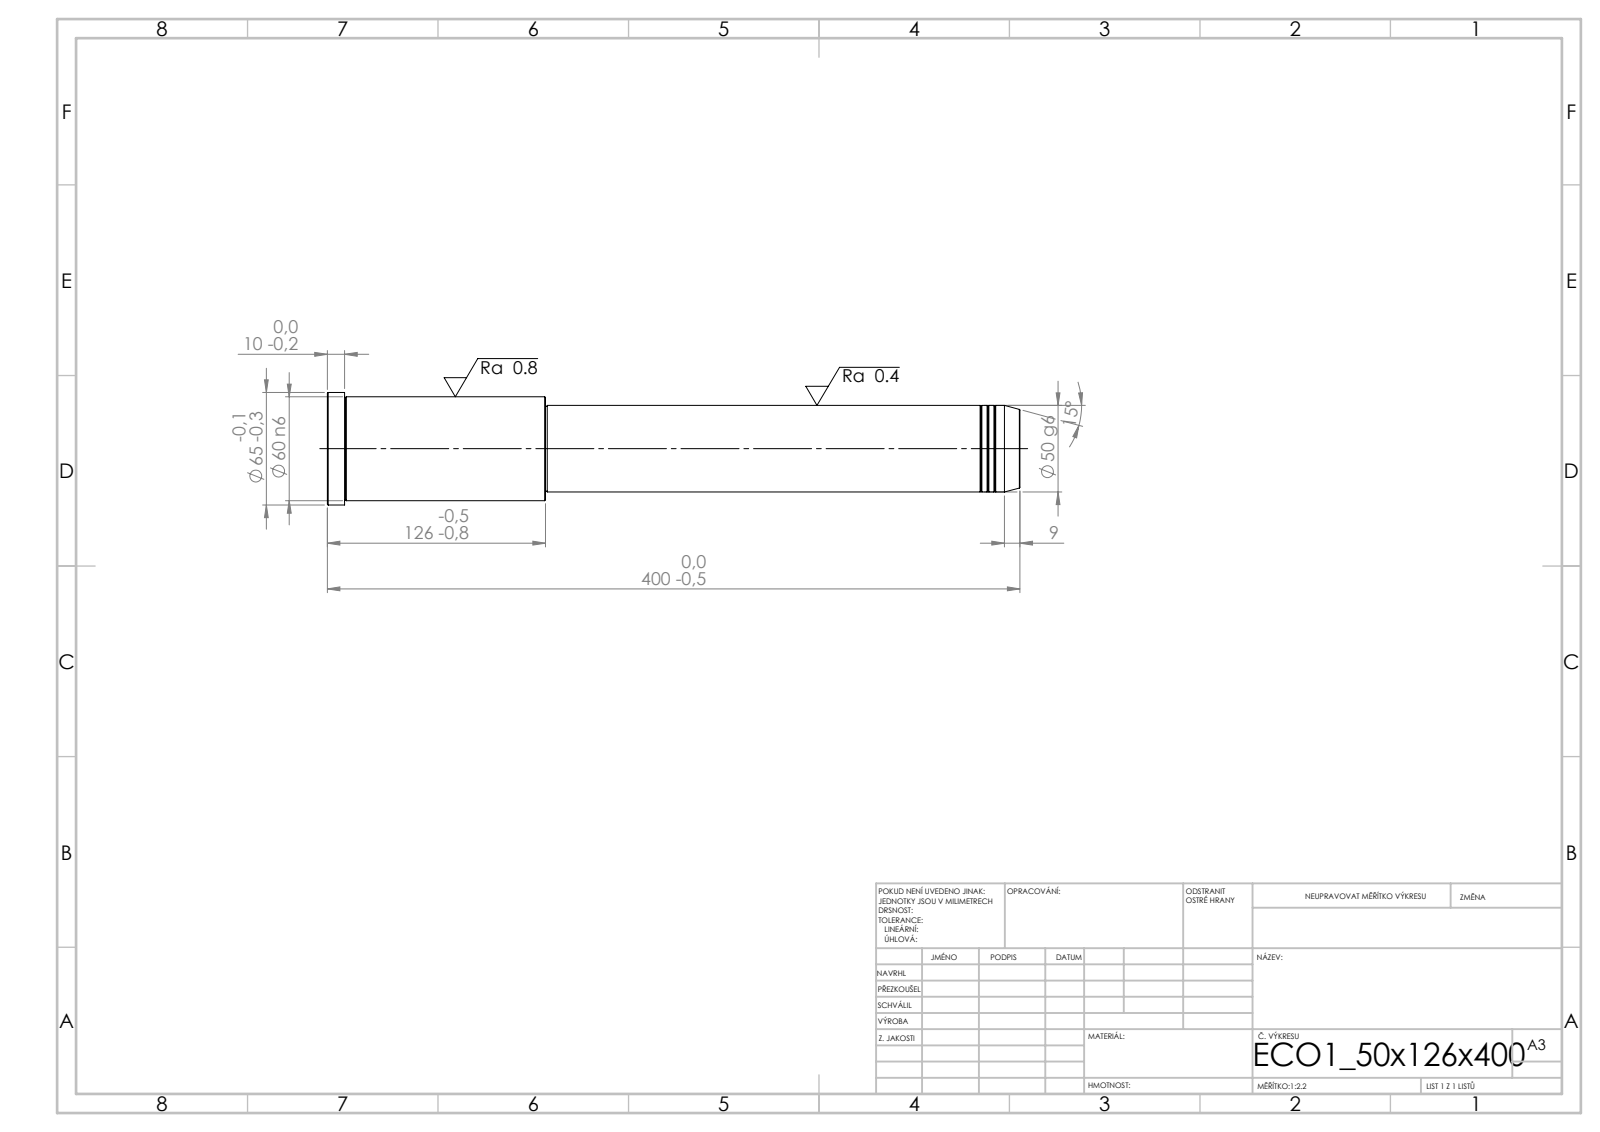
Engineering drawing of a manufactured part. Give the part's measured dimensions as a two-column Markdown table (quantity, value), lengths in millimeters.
| quantity | value |
| --- | --- |
| STEP written by | SolidWorks 2019 (CONFIG_CONTROL_DESIGN) |
| units | millimeters |
| bodies | 1 solid, 43 faces (5 planar, 14 cylindrical, 24 other) |
| overall size | 400 × 65 × 65 |
| volume | 897 126 mm³ |
| surface area | 73 587 mm² |
| round bosses / shafts (diameter × count) | 65 × 1, 60 × 1, 50 × 1, 49 × 1 |
| main face-to-face distances | 400, 274, 126, 390, 116, 10, 273, 1, 117, 127 |
